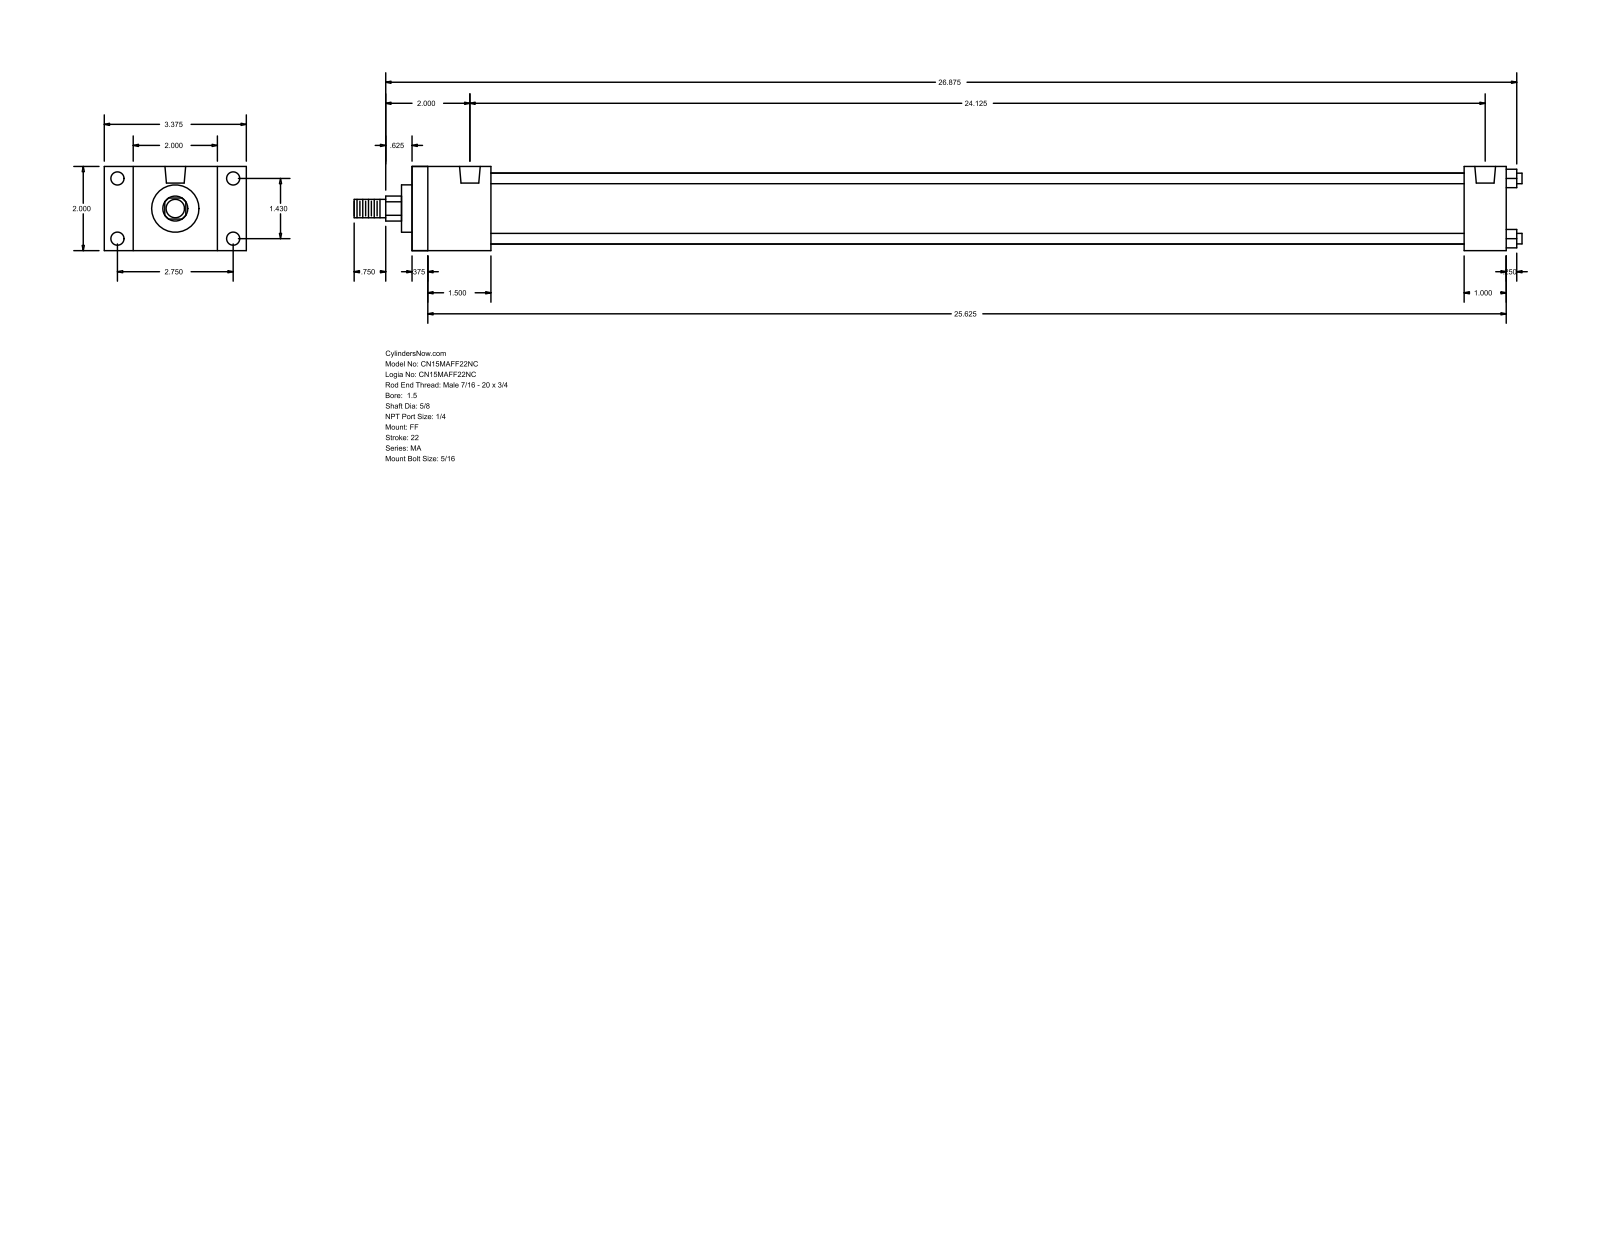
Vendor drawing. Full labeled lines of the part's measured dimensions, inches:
Part name (STEP PRODUCT): MA_FF__0150_0.625
STEP written by: GSSL Pune (CONFIG_CONTROL_DESIGN)
Units: inches
Bodies: 0 solids, 92 faces (64 planar, 28 cylindrical, 0 other)
Overall size (bounding box): 27.75 × 3.375 × 2
Round holes (diameter × count): ⌀0.313 ×8, ⌀0.492 ×2
Round bosses / shafts (diameter × count): ⌀0.25 ×4, ⌀1.69 ×1, ⌀1.125 ×1, ⌀0.625 ×1, ⌀0.437 ×1
Partial cylindrical surfaces — rounded edges, fillets, slot ends (radius × count): R0.297 ×1
Main face-to-face distances: 2, 26, 0.375, 25.625, 1.875, 25, 1.5, 24.625, 23.125, 24.125
Hole centre spacings: 1.43, 2.75, 3.099, 24.125
